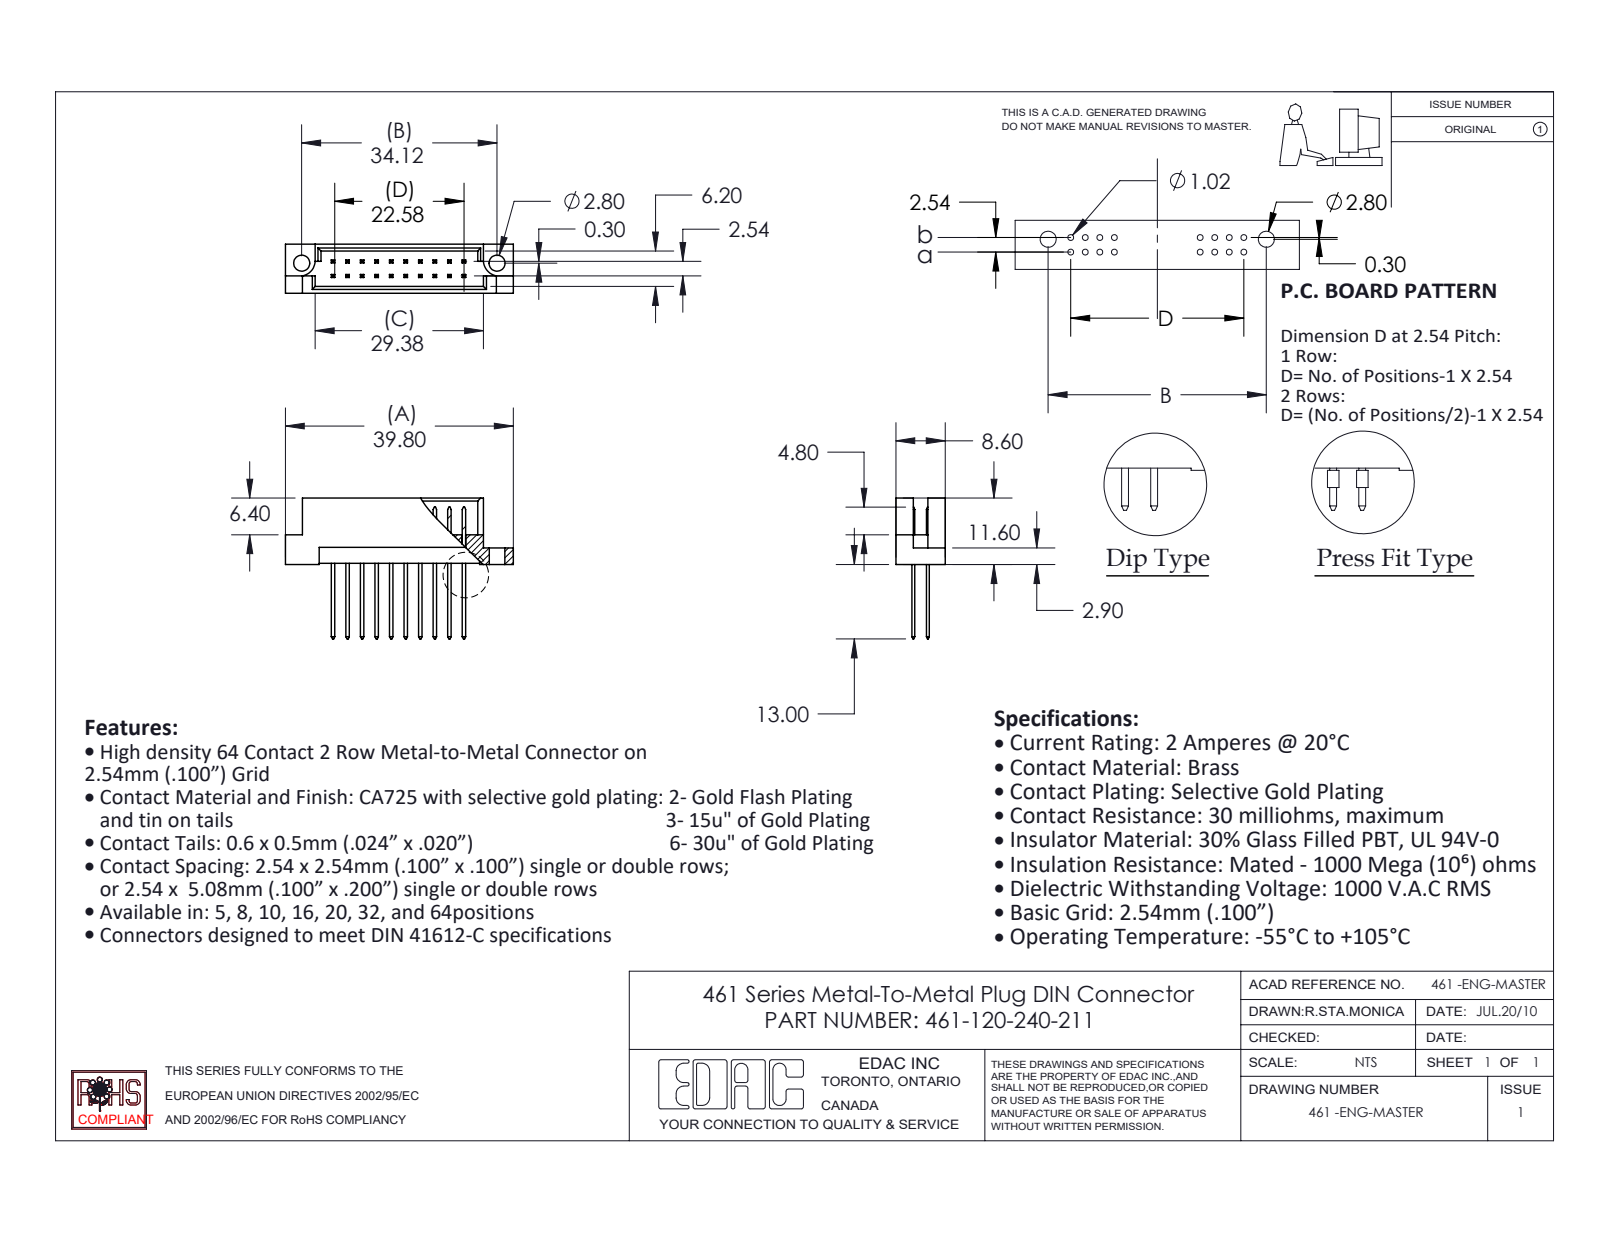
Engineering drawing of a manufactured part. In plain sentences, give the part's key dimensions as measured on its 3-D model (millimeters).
The part is named "461 Part_20; 461-120-240-211; 461-290_40". Its 3-D file was written by "SolidWorks 2020 (CONFIG_CONTROL_DESIGN)". It is 21 solids with 408 faces: 402 planar, 6 cylindrical and 0 other. Overall it measures 39.8 by 24.6 by 8.6 millimeters. Its volume is 2 040 cubic millimeters and its surface area 3 342 square millimeters. Round holes: 2 of diameter 2.8. Partial cylindrical surfaces (rounded edges, fillets, slot ends): 2 of radius 2.8. The main face-to-face distances are 2.54, 1.2, 7.4, 8.6, 3.28, 5.32, 2.08, 4.12, 2.78, 5.82. The hole center spacings are 34.12.
